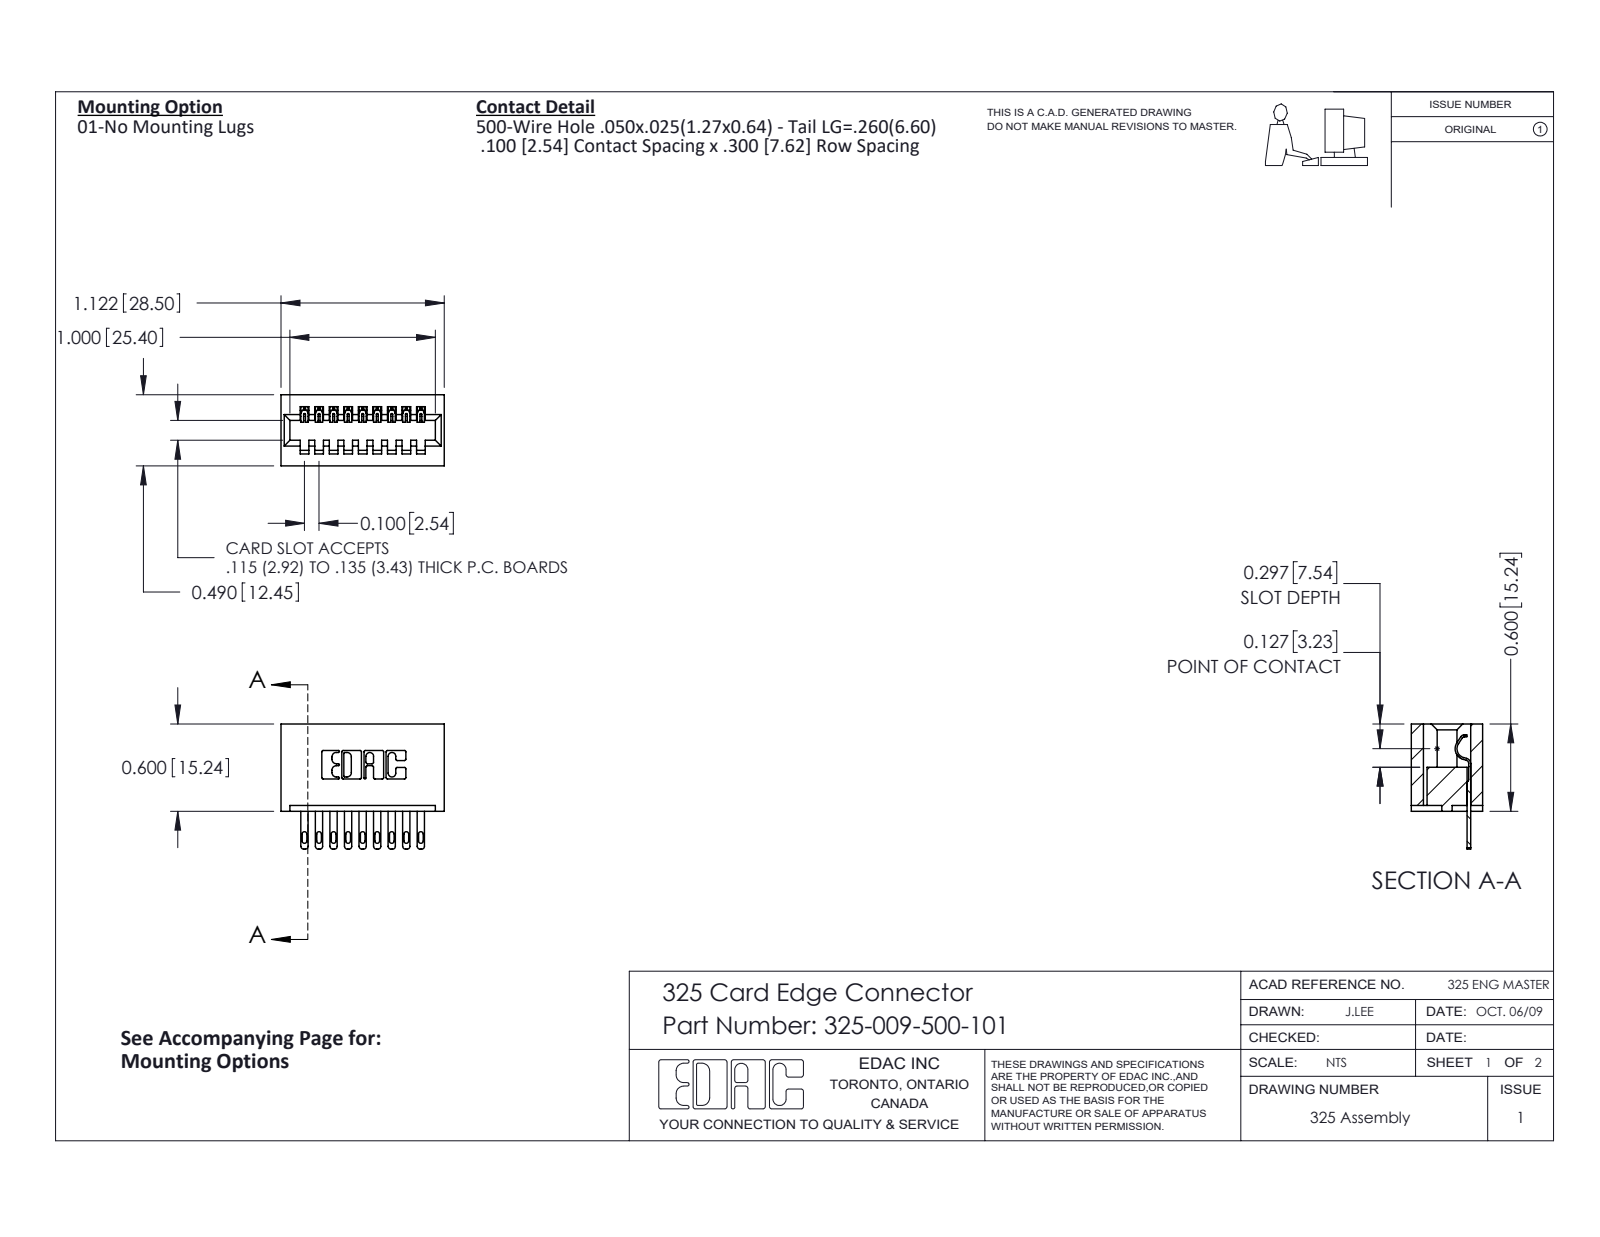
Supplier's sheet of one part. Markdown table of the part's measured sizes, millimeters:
| quantity | value |
| --- | --- |
| part name | 325 Part_Lugless; 325-009-500-101; 325-292-001_325-293-100 |
| STEP written by | SolidWorks 2016 (CONFIG_CONTROL_DESIGN) |
| units | millimeters |
| bodies | 10 solids, 592 faces (390 planar, 202 cylindrical, 0 other) |
| overall size | 28.5 × 21.8 × 12.4 |
| volume | 3 930 mm³ |
| surface area | 4 252 mm² |
| partial cylindrical surfaces (radius × count) | 0.3 × 22, 0.2 × 18, 0.4 × 18, 0.5 × 18, 0.2 × 6, 0.8 × 6, 0.7 × 3, 0.4 × 1 |
| main face-to-face distances | 7.6, 2.5, 5.1, 2.1, 10.3, 10.2, 1, 1.5, 12.4, 12.7 |
